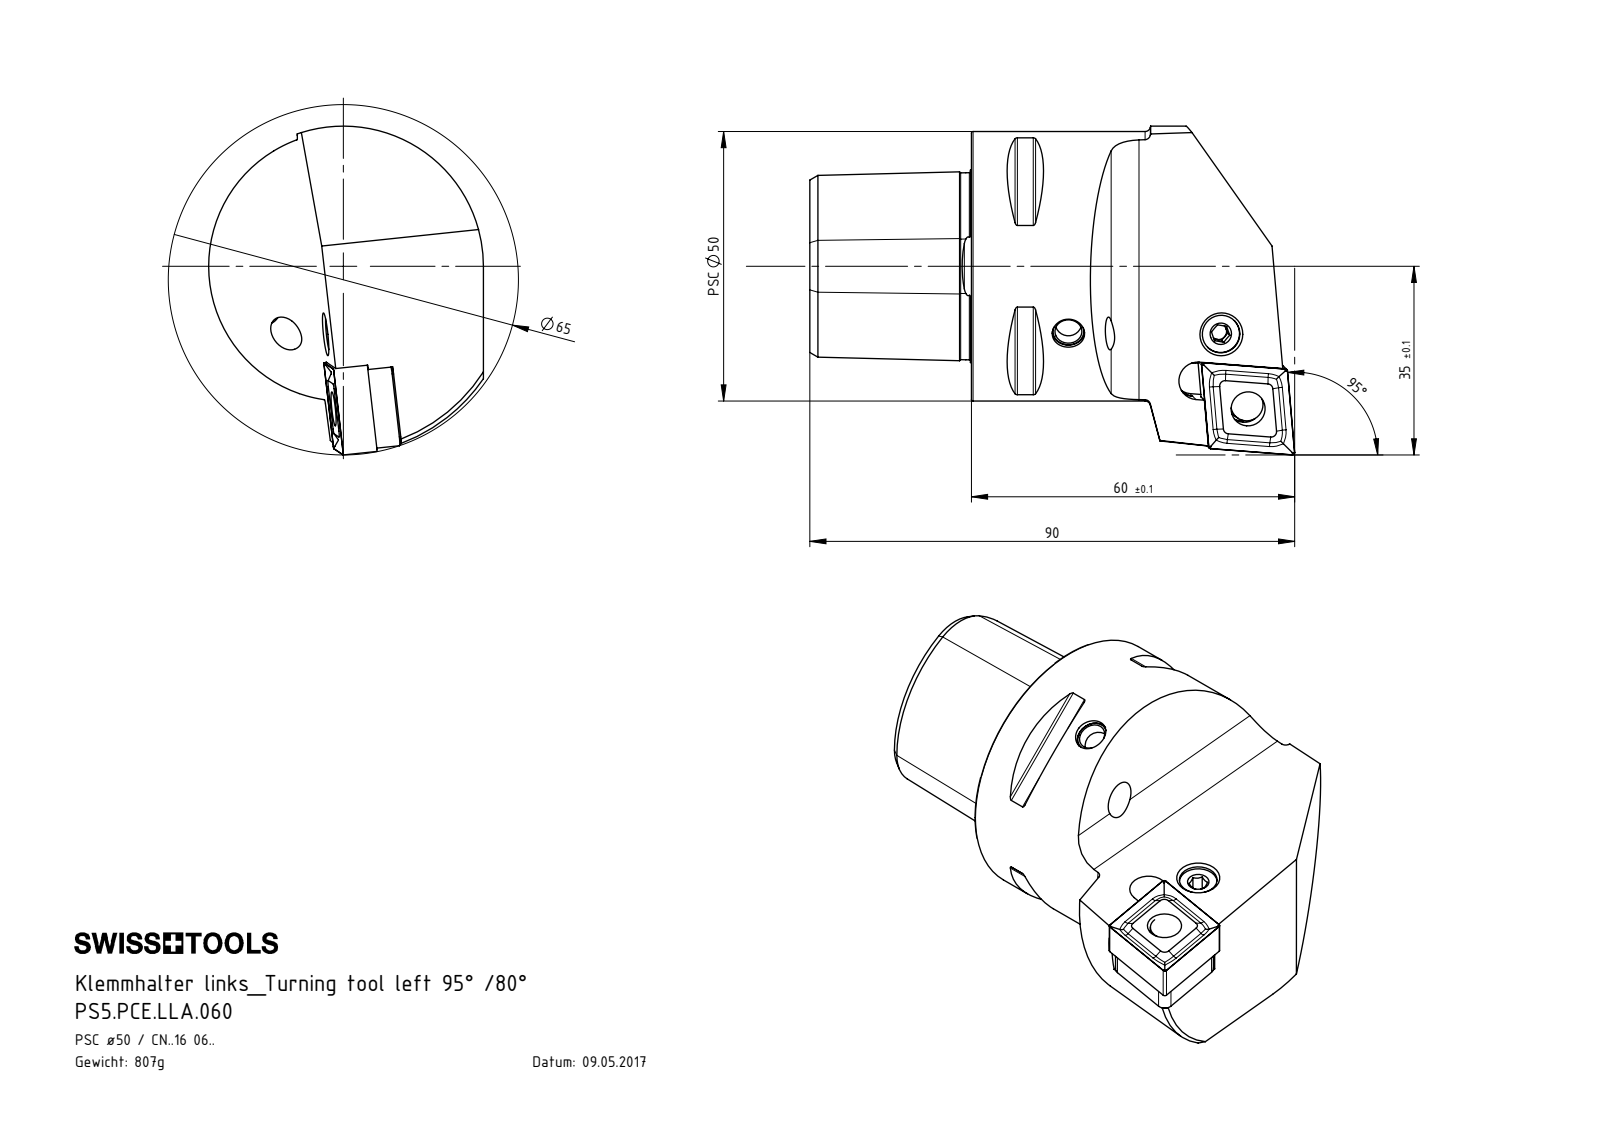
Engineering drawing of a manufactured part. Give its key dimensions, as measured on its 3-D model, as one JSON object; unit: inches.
{"part_name": "PS5.PCE.LLA.060; KVT_MB_600_060; WCE-ER3.101.000_A; WCE-ER2.101.004_A (+3 more)", "step_written_by": "SolidWorks 2017 (AUTOMOTIVE_DESIGN)", "units": "inches", "bodies": {"solids": 7, "faces": 245, "planar": 90, "cylindrical": 52, "other": 103}, "overall_size": [3.543, 2.402, 2.008], "volume_in3": 6.196, "surface_area_in2": 36.16, "round_holes": [[0.197, 2], [0.157, 1], [0.24, 1], [0.25, 1], [0.276, 1], [0.317, 1], [0.331, 1], [0.571, 1], [0.827, 1], [0.945, 1]], "round_bosses_or_shafts": [[0.236, 2], [1.969, 1], [0.315, 1], [0.311, 1], [0.252, 1], [0.14, 1]], "partial_cylinders_radius": [[0.02, 8], [0.016, 4], [0.059, 4], [0.138, 3], [0.012, 2], [0.157, 2], [0.118, 1], [0.122, 1]], "face_to_face_distances": [1.181, 0.187, 0.231, 0.755, 0.594, 0.418, 0.594, 0.188, 0.23, 1.748], "hole_center_spacings": [0.581, 0.59, 1.024]}
